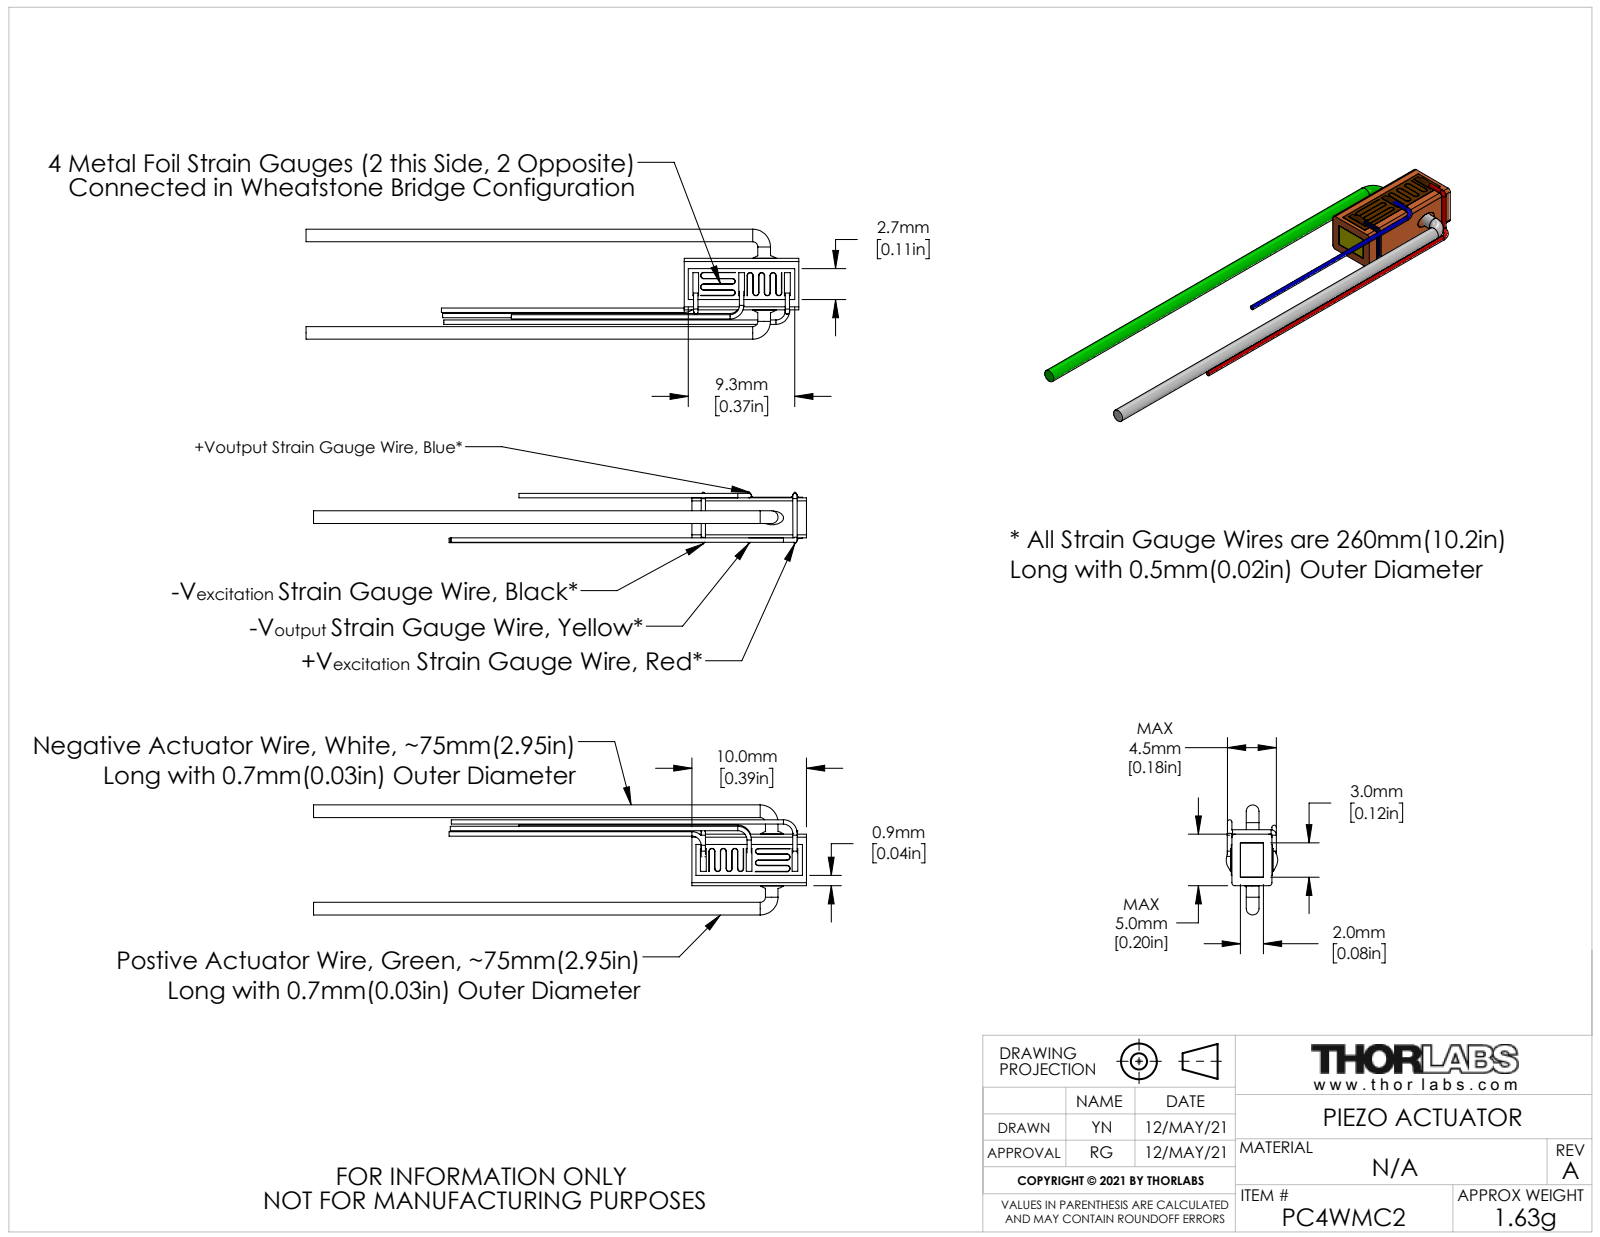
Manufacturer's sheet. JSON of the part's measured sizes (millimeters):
{"part_name": "CTN017646-E0W", "step_written_by": "SolidWorks 2018 (AUTOMOTIVE_DESIGN)", "units": "millimeters", "bodies": {"solids": 12, "faces": 244, "planar": 124, "cylindrical": 88, "other": 32}, "overall_size": [43.03, 9.6, 4.5], "volume_mm3": 254, "surface_area_mm2": 936, "round_bosses_or_shafts": [[0.38, 13], [1.1, 3]], "partial_cylinders_radius": [[0.23, 12], [0.27, 12], [0.25, 8], [0.22, 4], [0.27, 4], [0.28, 4]], "face_to_face_distances": [0.75, 2.75, 3.5, 2, 3.75, 0.8, 2.8, 3.55, 3, 4.5]}
